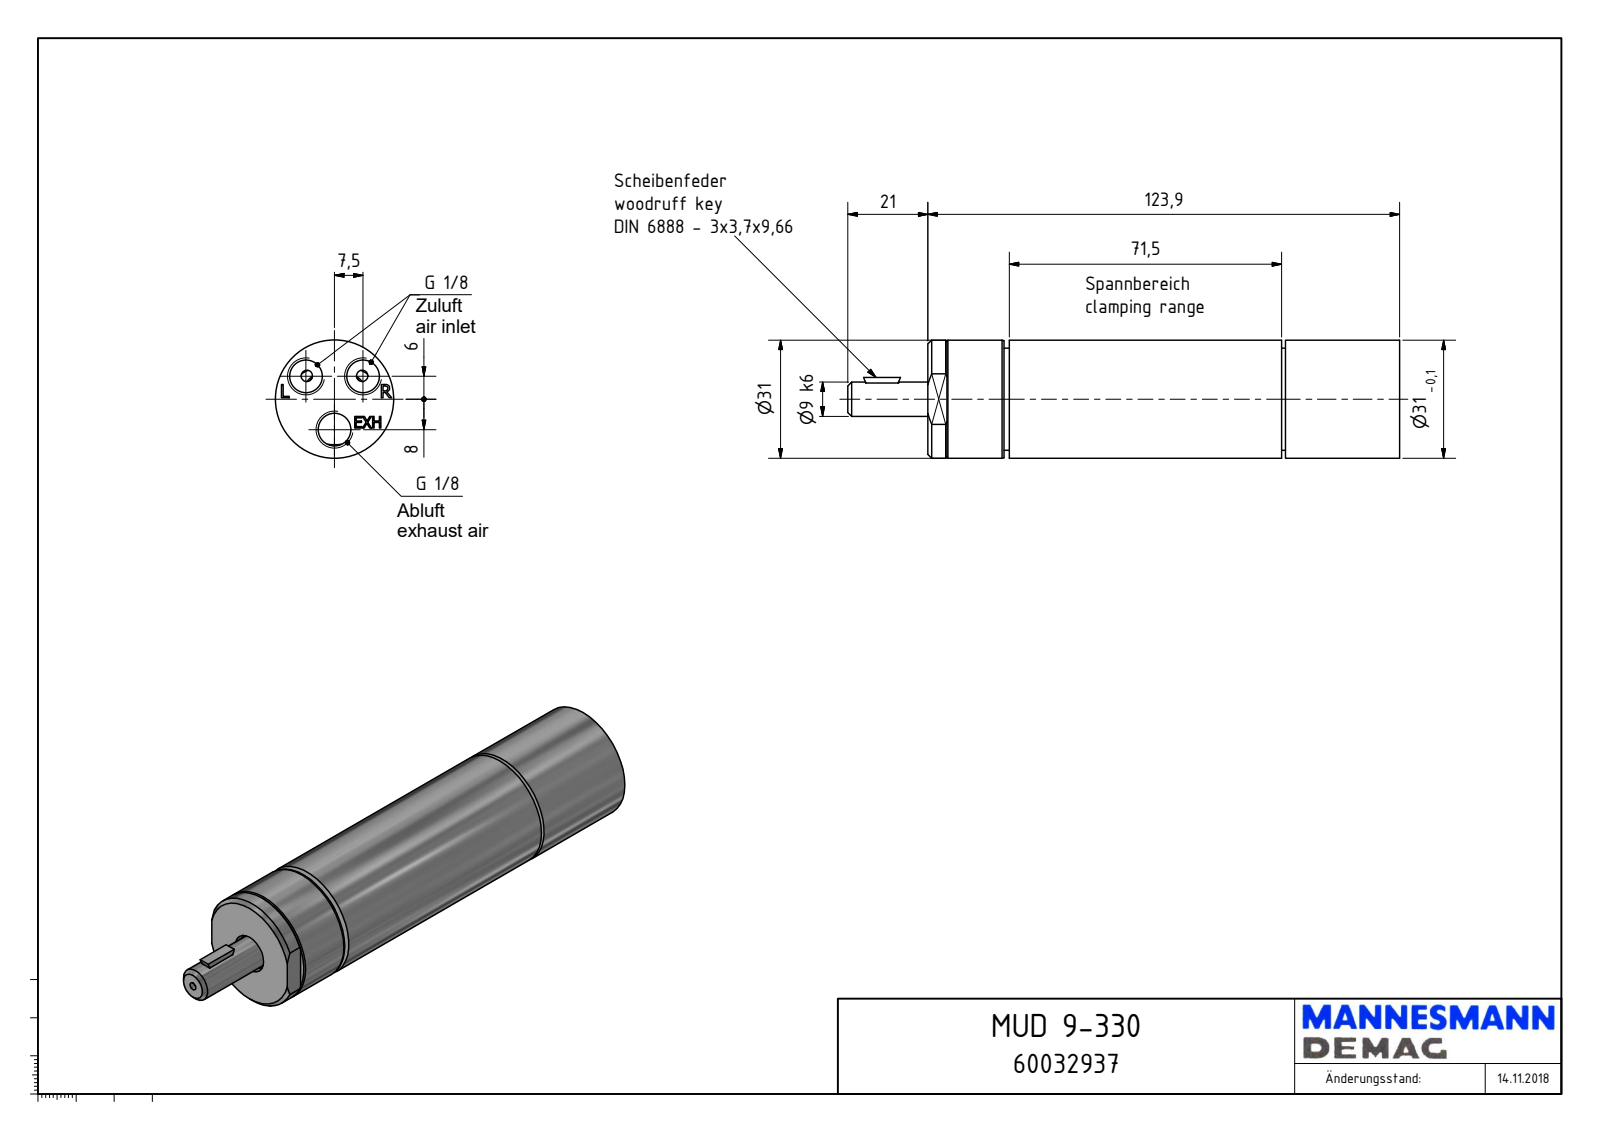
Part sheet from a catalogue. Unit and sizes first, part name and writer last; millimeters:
Units: millimetres
Overall size (bounding box): 144.9 × 31 × 31
Round holes (diameter × count): ⌀8.57 ×3, ⌀1 ×1, ⌀10.5 ×1, ⌀29.3 ×1
Round bosses / shafts (diameter × count): ⌀31 ×1, ⌀28 ×1, ⌀26.79 ×1, ⌀9 ×1
Partial cylindrical surfaces — rounded edges, fillets, slot ends (radius × count): R4 ×8, R5 ×1, R5.25 ×1, R12.57 ×1, R12.75 ×1, R14.39 ×1
Main face-to-face distances: 123.9, 21.4, 102.5, 92.9, 71.5, 31, 116.27, 94.87, 23.37, 7.63
Hole centre spacings: 9.6, 15.88, 8, 15
Volume: 92 590 mm³ · Surface area: 17 332 mm²
Bodies: 1 solid, 151 faces (94 planar, 37 cylindrical, 20 other)
Part name (STEP PRODUCT): MUD 9-330_60032937
STEP written by: Autodesk Inventor 2018 (AUTOMOTIVE_DESIGN)
